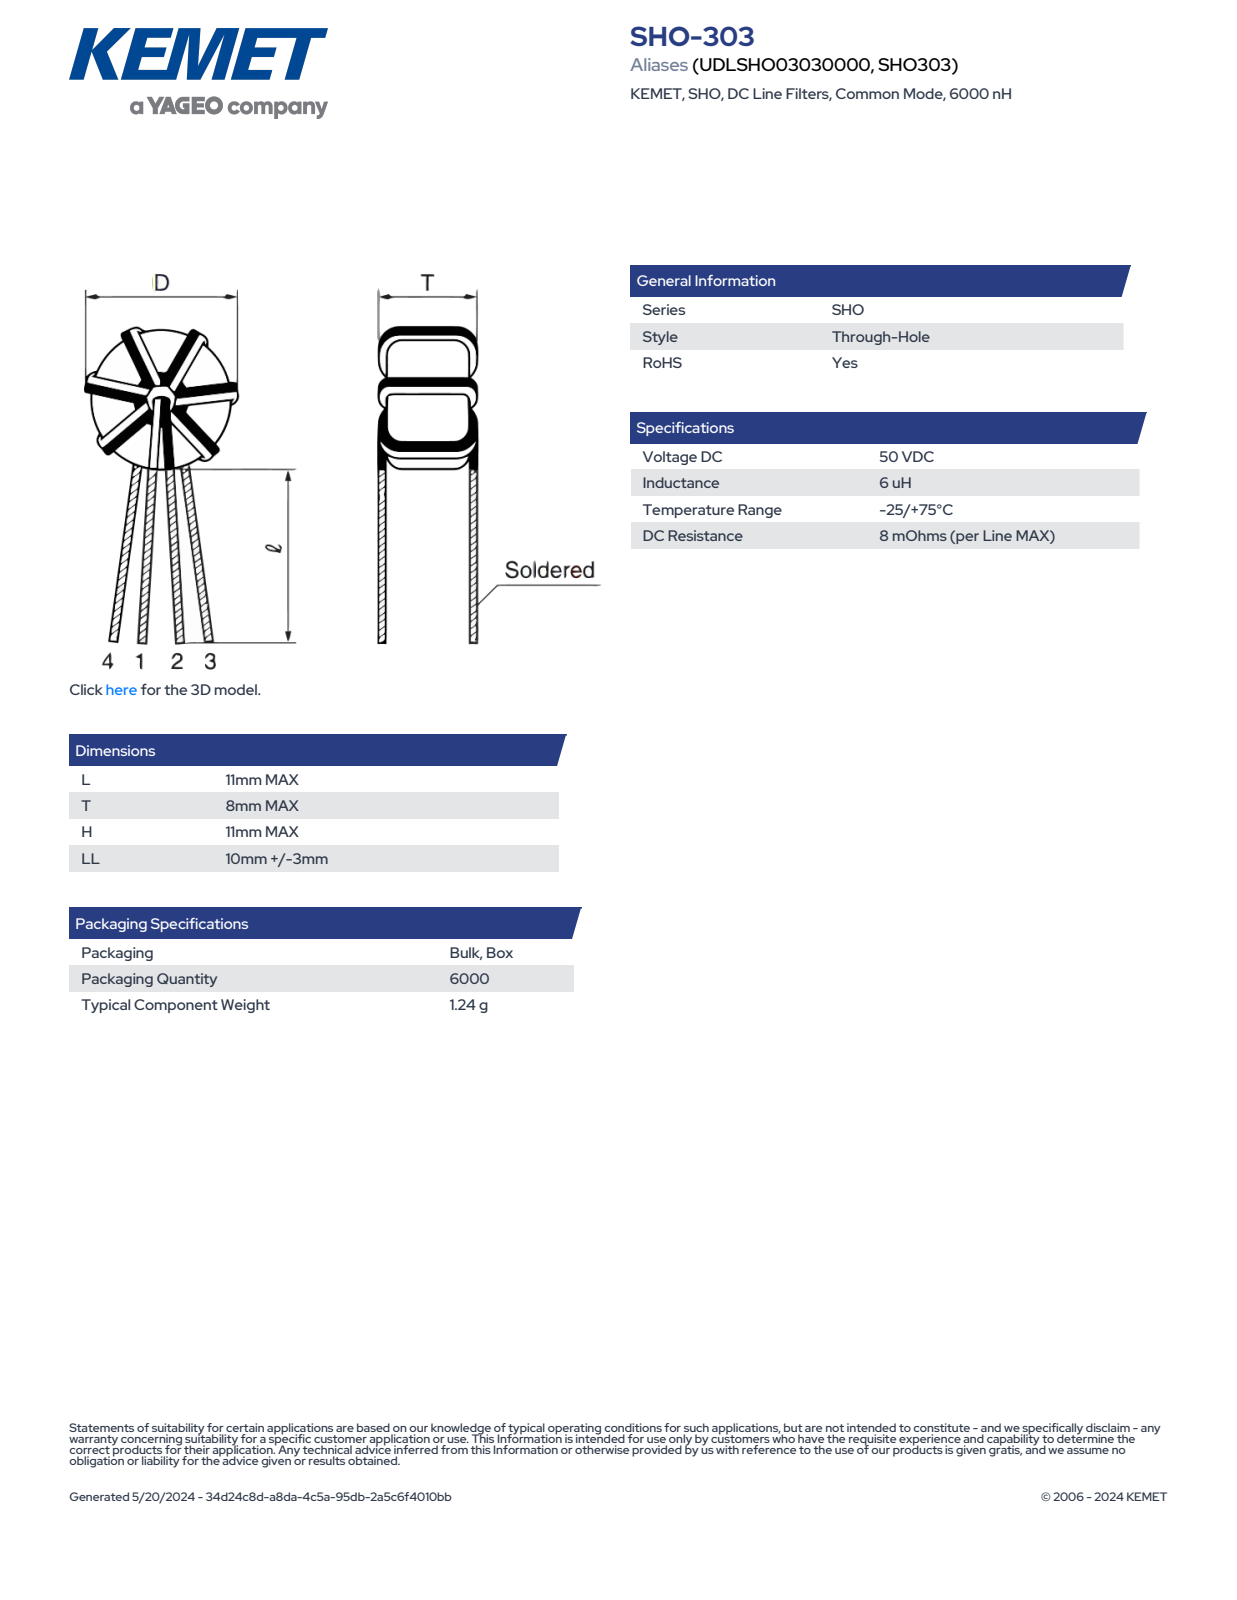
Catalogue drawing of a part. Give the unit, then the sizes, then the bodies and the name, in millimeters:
Units: millimetres
Overall size (bounding box): 23.65 × 11 × 8
Round holes (diameter × count): ⌀3.4 ×1
Round bosses / shafts (diameter × count): ⌀0.3 ×48, ⌀0.3 ×4, ⌀10.3 ×1
Partial cylindrical surfaces — rounded edges, fillets, slot ends (radius × count): R0.15 ×16
Main face-to-face distances: 7.3
Volume: 572 mm³ · Surface area: 857 mm²
Bodies: 17 solids, 398 faces (6 planar, 264 cylindrical, 128 other)
Part name (STEP PRODUCT): IFC_NTSHO_L11T8LL13
STEP written by: SolidWorks 2014 (AUTOMOTIVE_DESIGN)
